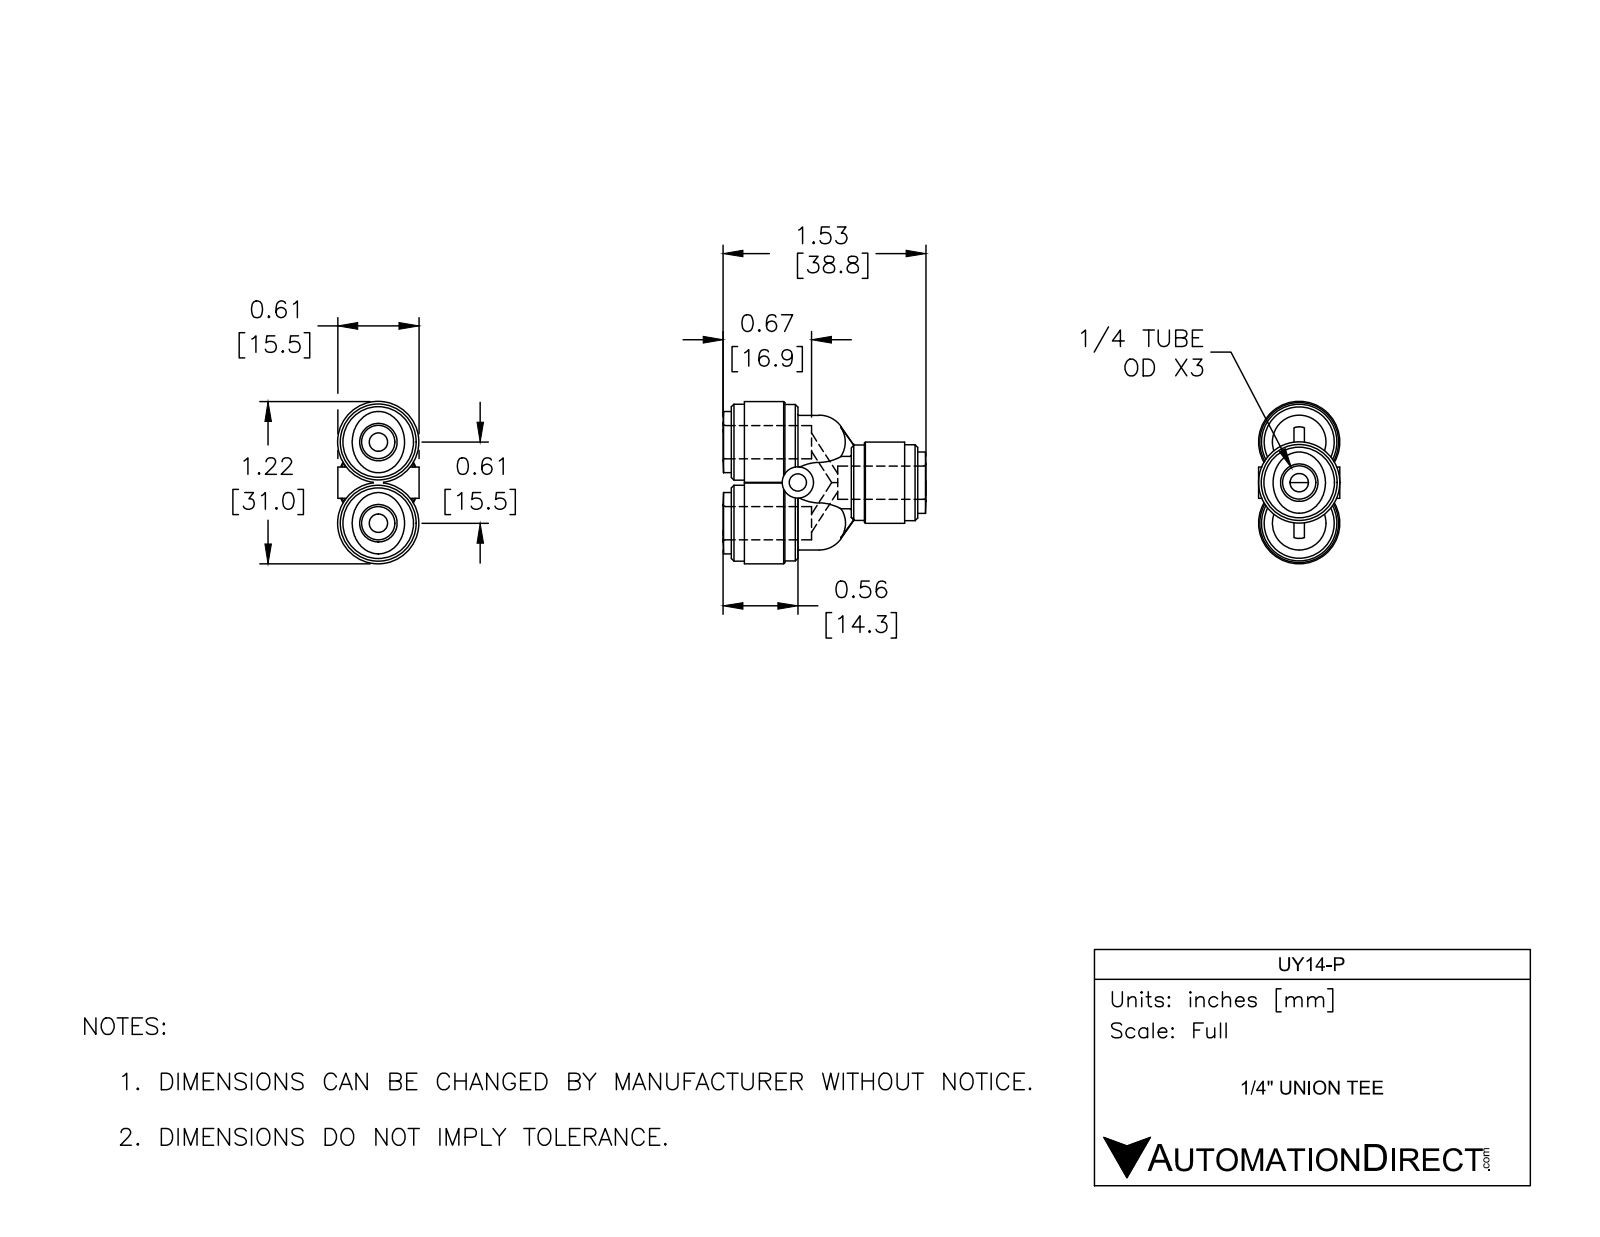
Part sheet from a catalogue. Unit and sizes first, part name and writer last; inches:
Units: inches
Overall size (bounding box): 1.528 × 1.22 × 0.61
Round holes (diameter × count): ⌀0.25 ×3, ⌀0.13 ×1
Round bosses / shafts (diameter × count): ⌀0.61 ×3, ⌀0.571 ×3, ⌀0.567 ×3, ⌀0.402 ×3, ⌀0.236 ×1
Main face-to-face distances: 0.5, 0.402, 0.902, 0.098, 1.303, 0.803, 0.602, 0.799, 0.504, 0.102
Hole centre spacings: 0.305, 0.61
Volume: 0.459 in³ · Surface area: 7.341 in²
Bodies: 1 solid, 123 faces (23 planar, 40 cylindrical, 60 other)
Part name (STEP PRODUCT): UY14-P
STEP written by: SolidWorks 2017 (AUTOMOTIVE_DESIGN)
